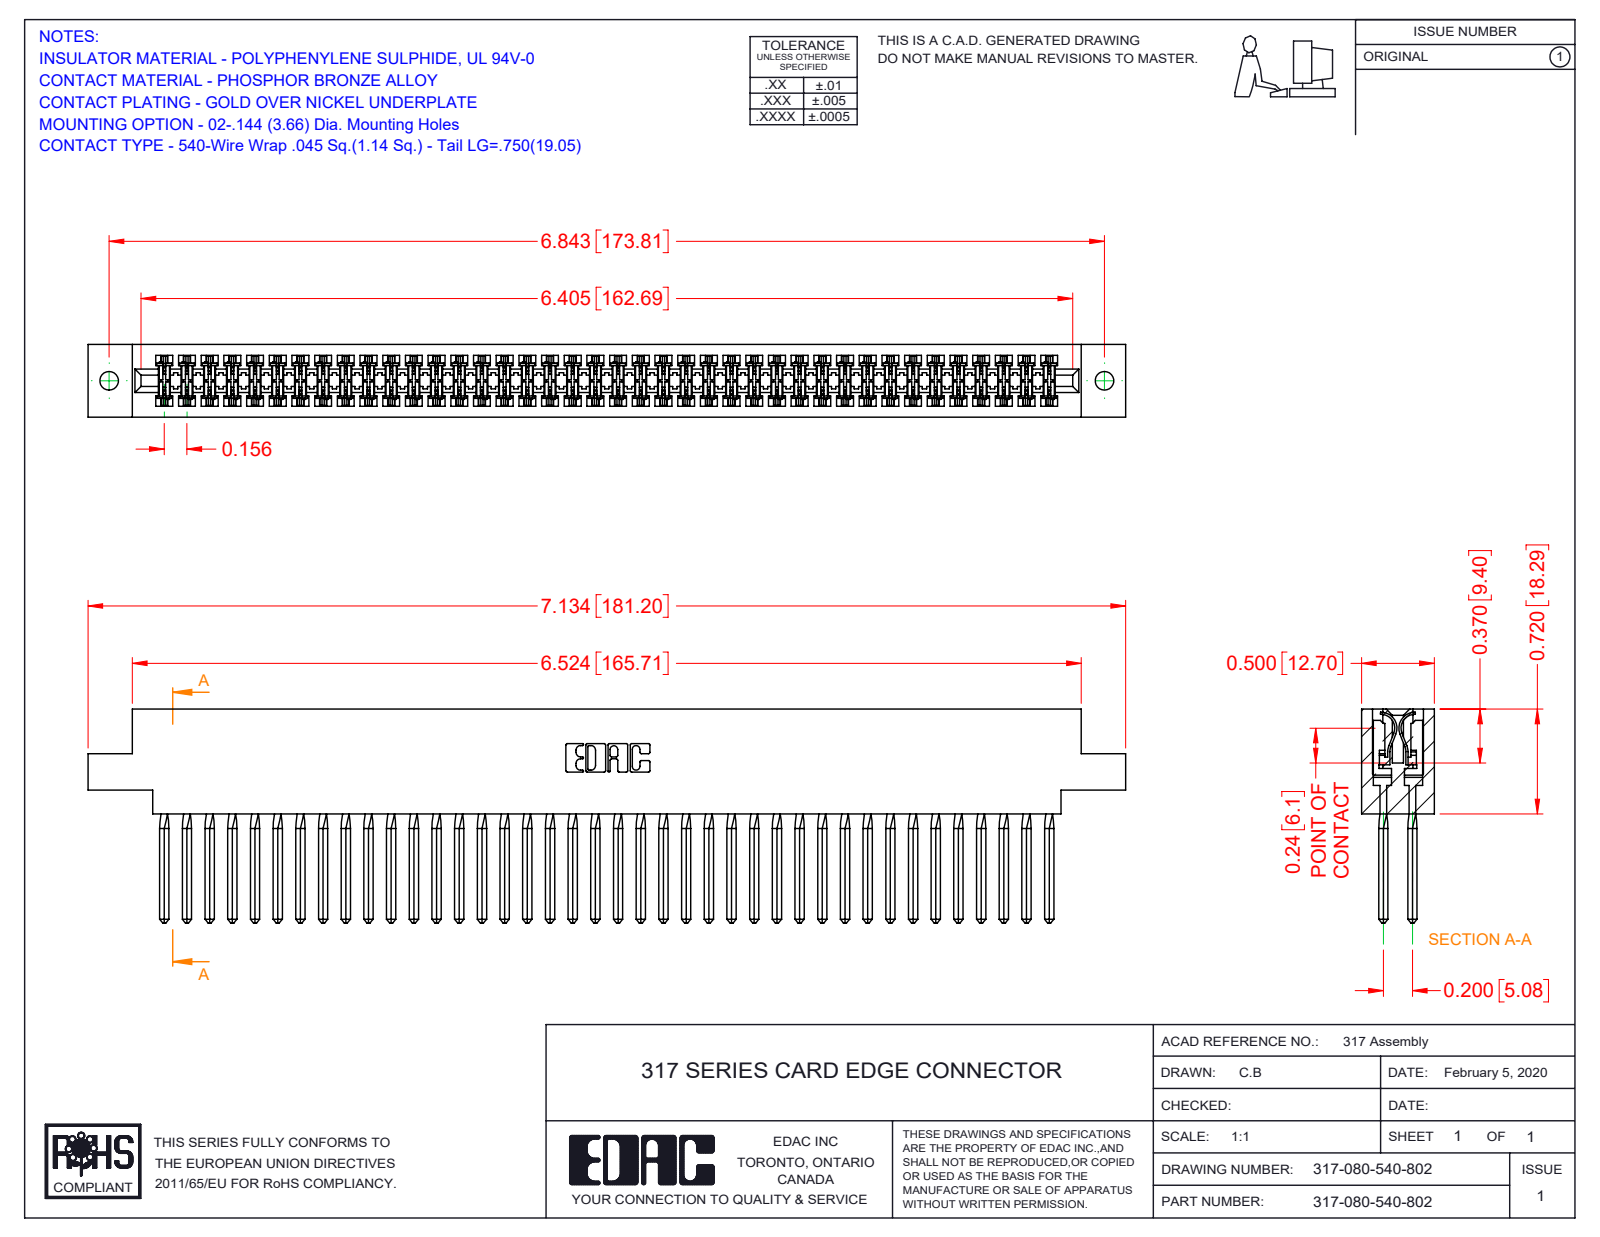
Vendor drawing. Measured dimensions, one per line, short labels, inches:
name: 317-290-001_540; 317 Part_.144 Dia; 317-080-540-802
written by: SolidWorks 2016 (CONFIG_CONTROL_DESIGN)
unit: in
bodies: 81 solids, 7222 faces (5898 planar, 1004 cylindrical, 320 other)
size: 7.134 × 1.47 × 0.5
volume: 1.849 in³; area: 69.51 in²
holes: 2× ⌀0.128
rounds: 160× R0.015, 22× R0.01, 6× R0.007, 6× R0.031, 3× R0.026, 2× R0.095, 2× R0.1, 2× R0.11
face distances: 0.5, 0.075, 0.425, 0.35, 0.195, 0.094, 0.2, 0.115, 0.131, 0.11
hole spacings: 6.843
